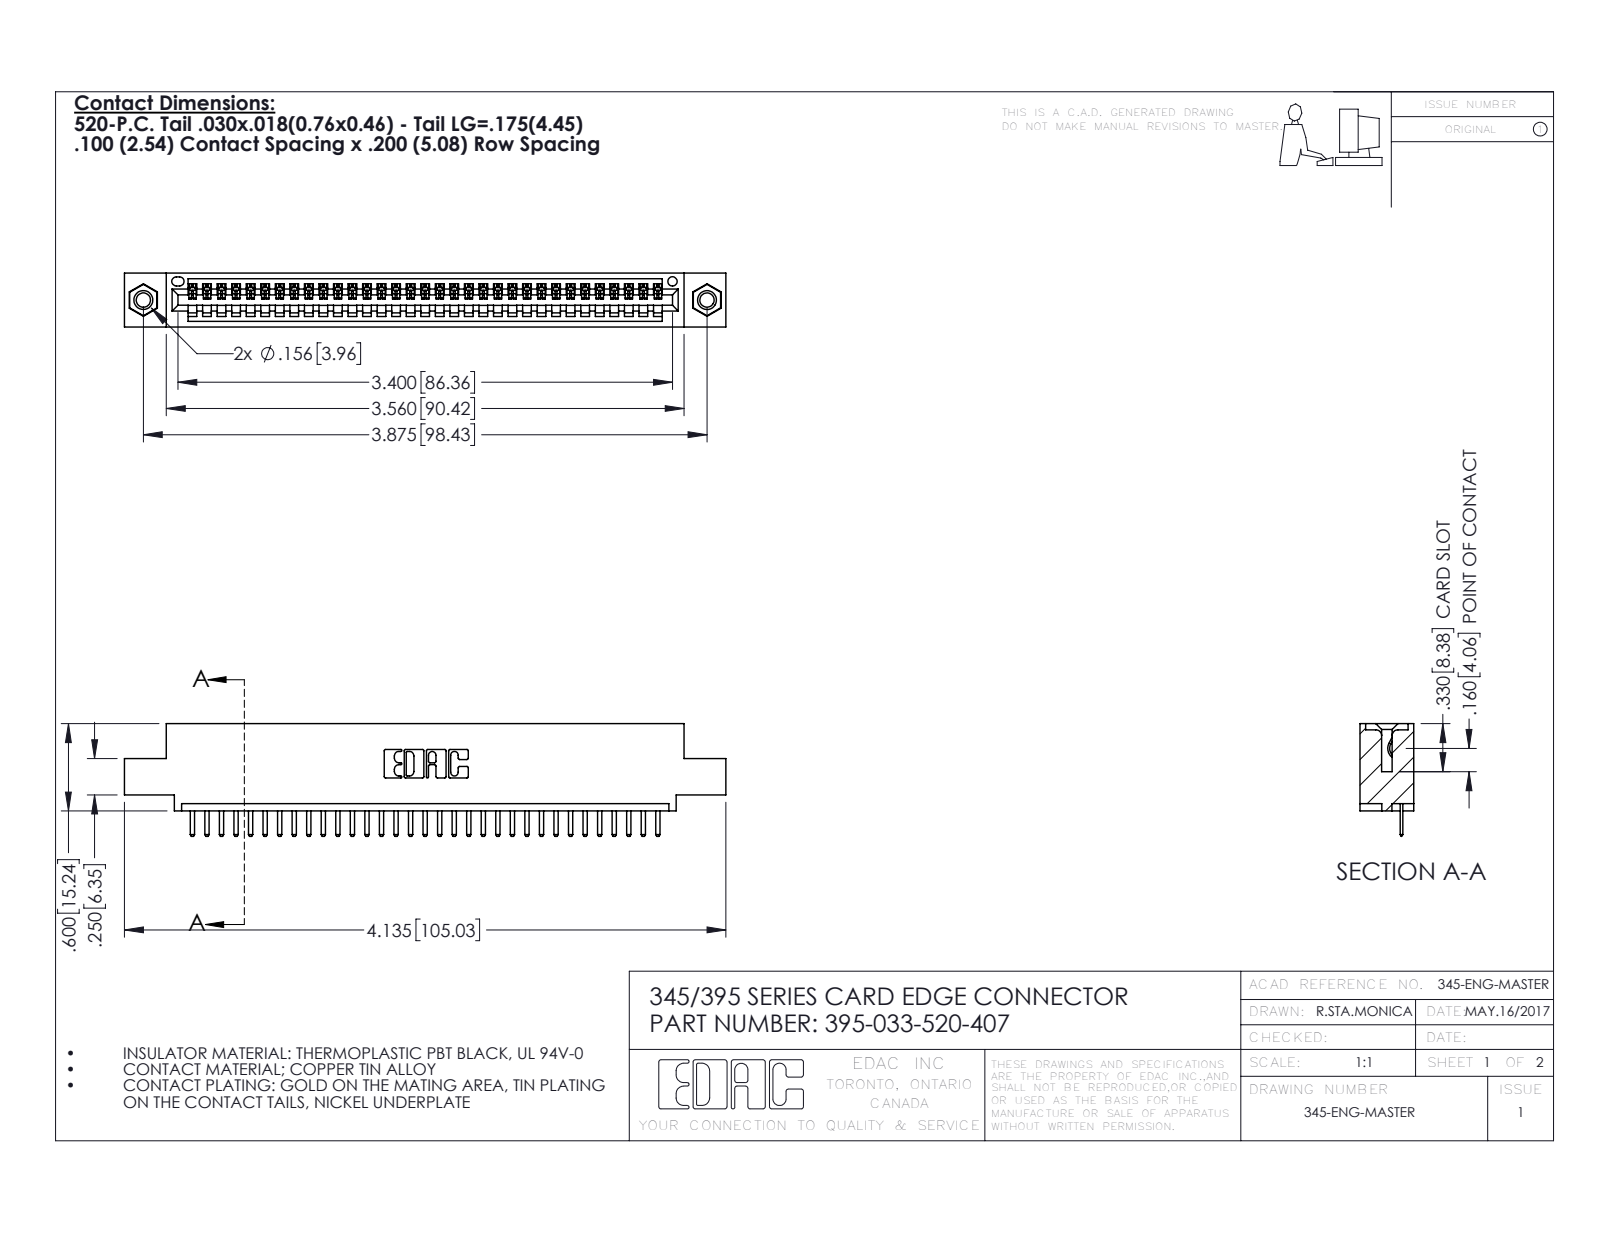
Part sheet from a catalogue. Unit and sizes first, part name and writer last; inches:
Units: inches
Overall size (bounding box): 4.135 × 0.775 × 0.37
Round holes (diameter × count): ⌀0.098 ×2, ⌀0.125 ×2, ⌀0.156 ×2, ⌀0.064 ×1
Round bosses / shafts (diameter × count): ⌀0.155 ×2
Partial cylindrical surfaces — rounded edges, fillets, slot ends (radius × count): R0.01 ×68, R0.006 ×66, R0.01 ×22, R0.007 ×6, R0.031 ×6, R0.026 ×3, R0.031 ×2, R0.04 ×2
Main face-to-face distances: 0.072, 0.298, 0.37, 0.2, 0.098, 0.272, 0.025, 0.225, 0.072, 0.149
Hole centre spacings: 0.27, 3.64, 3.875
Volume: 0.593 in³ · Surface area: 19.53 in²
Bodies: 36 solids, 2236 faces (1502 planar, 718 cylindrical, 16 other)
Part name (STEP PRODUCT): 395-033-520-407; 345-250-001_345-250-005-103; 345-292-001_345-293-120; 345 Part_0.110 Offset - 0.156 Dia-TI
STEP written by: SolidWorks 2016 (CONFIG_CONTROL_DESIGN)
